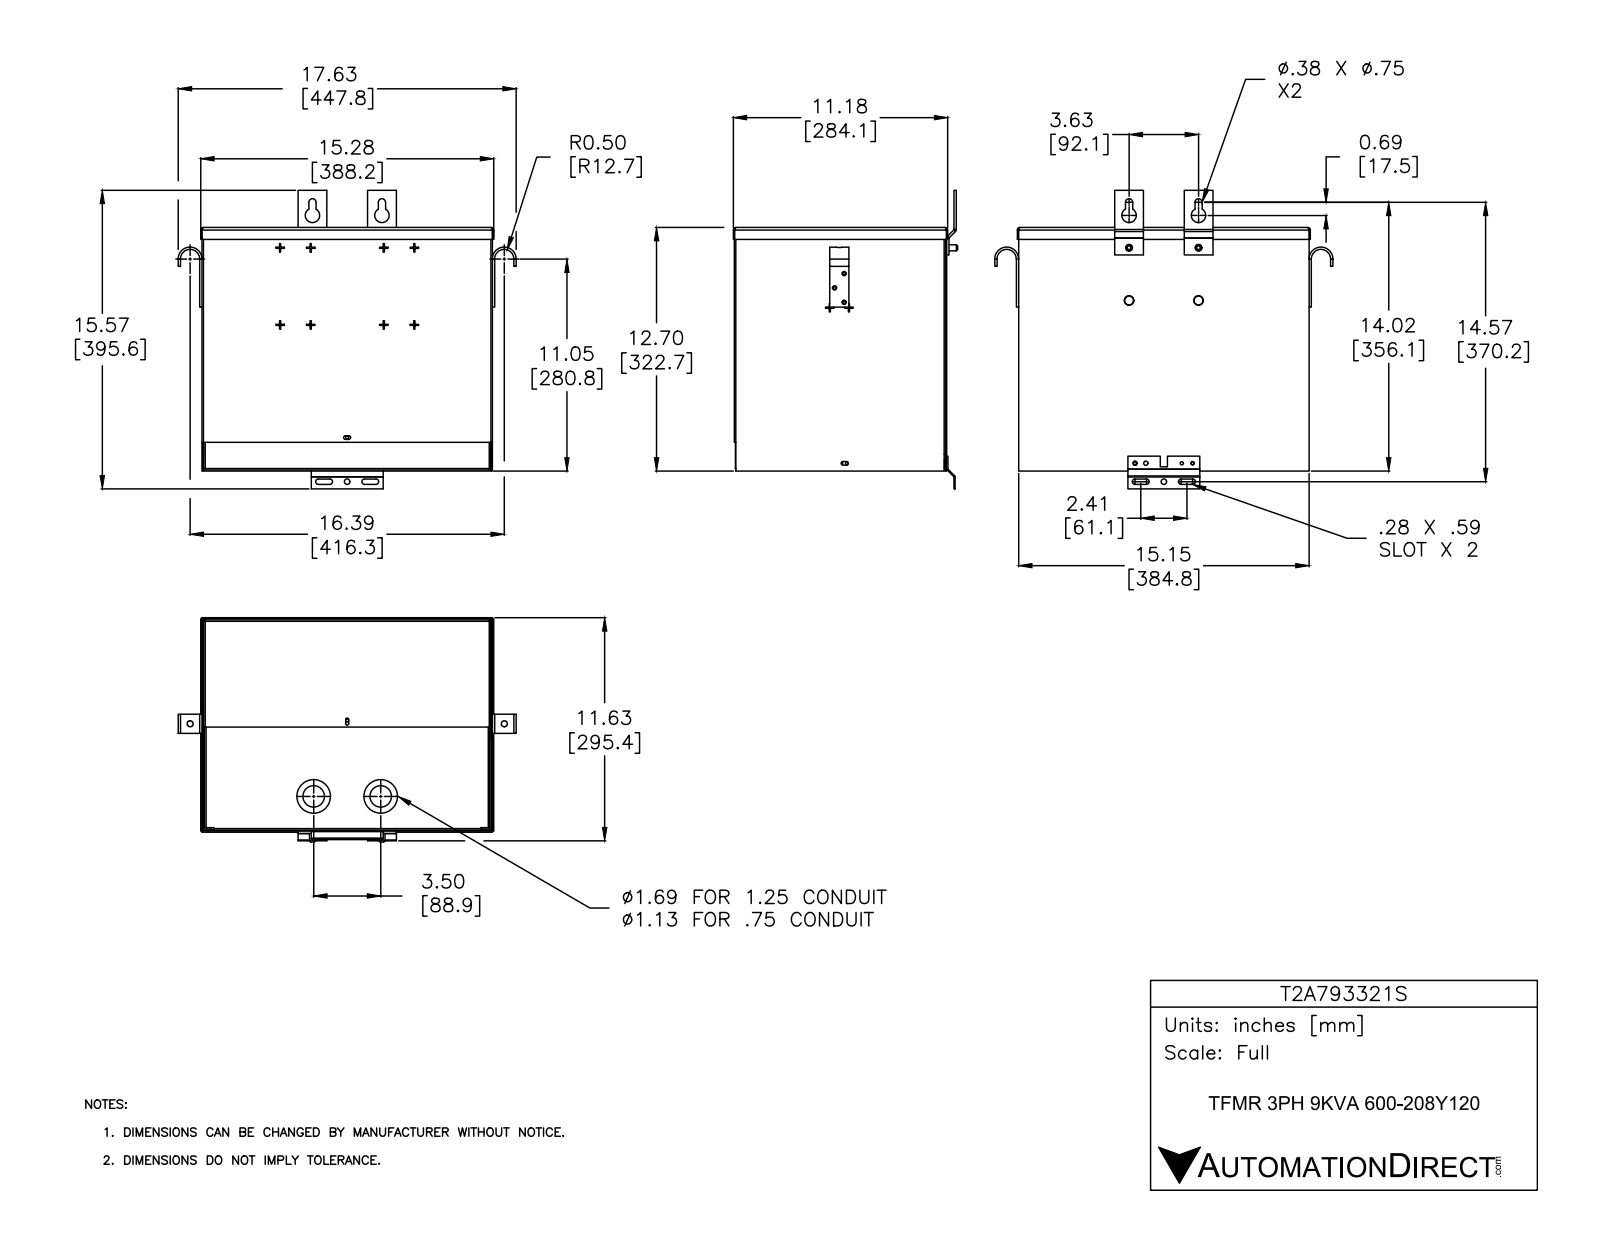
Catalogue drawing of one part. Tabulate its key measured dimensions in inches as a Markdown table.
| quantity | value |
| --- | --- |
| part name | T2A793321S |
| STEP written by | SolidWorks 2015 (AUTOMOTIVE_DESIGN) |
| units | inches |
| bodies | 12 solids, 707 faces (499 planar, 138 cylindrical, 70 other) |
| overall size | 17.63 × 15.574 × 11.697 |
| volume | 66.19 in³ |
| surface area | 2 202 in² |
| round holes (diameter × count) | 0.16 × 5, 0.313 × 4, 0.172 × 2, 0.219 × 2, 0.281 × 2, 0.344 × 2, 0.75 × 2, 1.125 × 2, 1.75 × 2, 0.173 × 1, 0.187 × 1 |
| round bosses / shafts (diameter × count) | 1.81 × 2, 1.185 × 2, 0.312 × 2 |
| partial cylindrical surfaces (radius × count) | 0.015 × 12, 0.075 × 12, 0.094 × 8, 0.075 × 4, 0.135 × 4, 0.141 × 4, 0.02 × 2, 0.03 × 2 |
| main face-to-face distances | 0.06, 11.02, 15.09, 10.96, 11.08, 12.52, 12.587, 0.067, 15.15, 15.03 |
| hole center spacings | 0.563, 1.342, 1.638, 1.688, 1.781, 2.014, 2.437, 3.625 |
